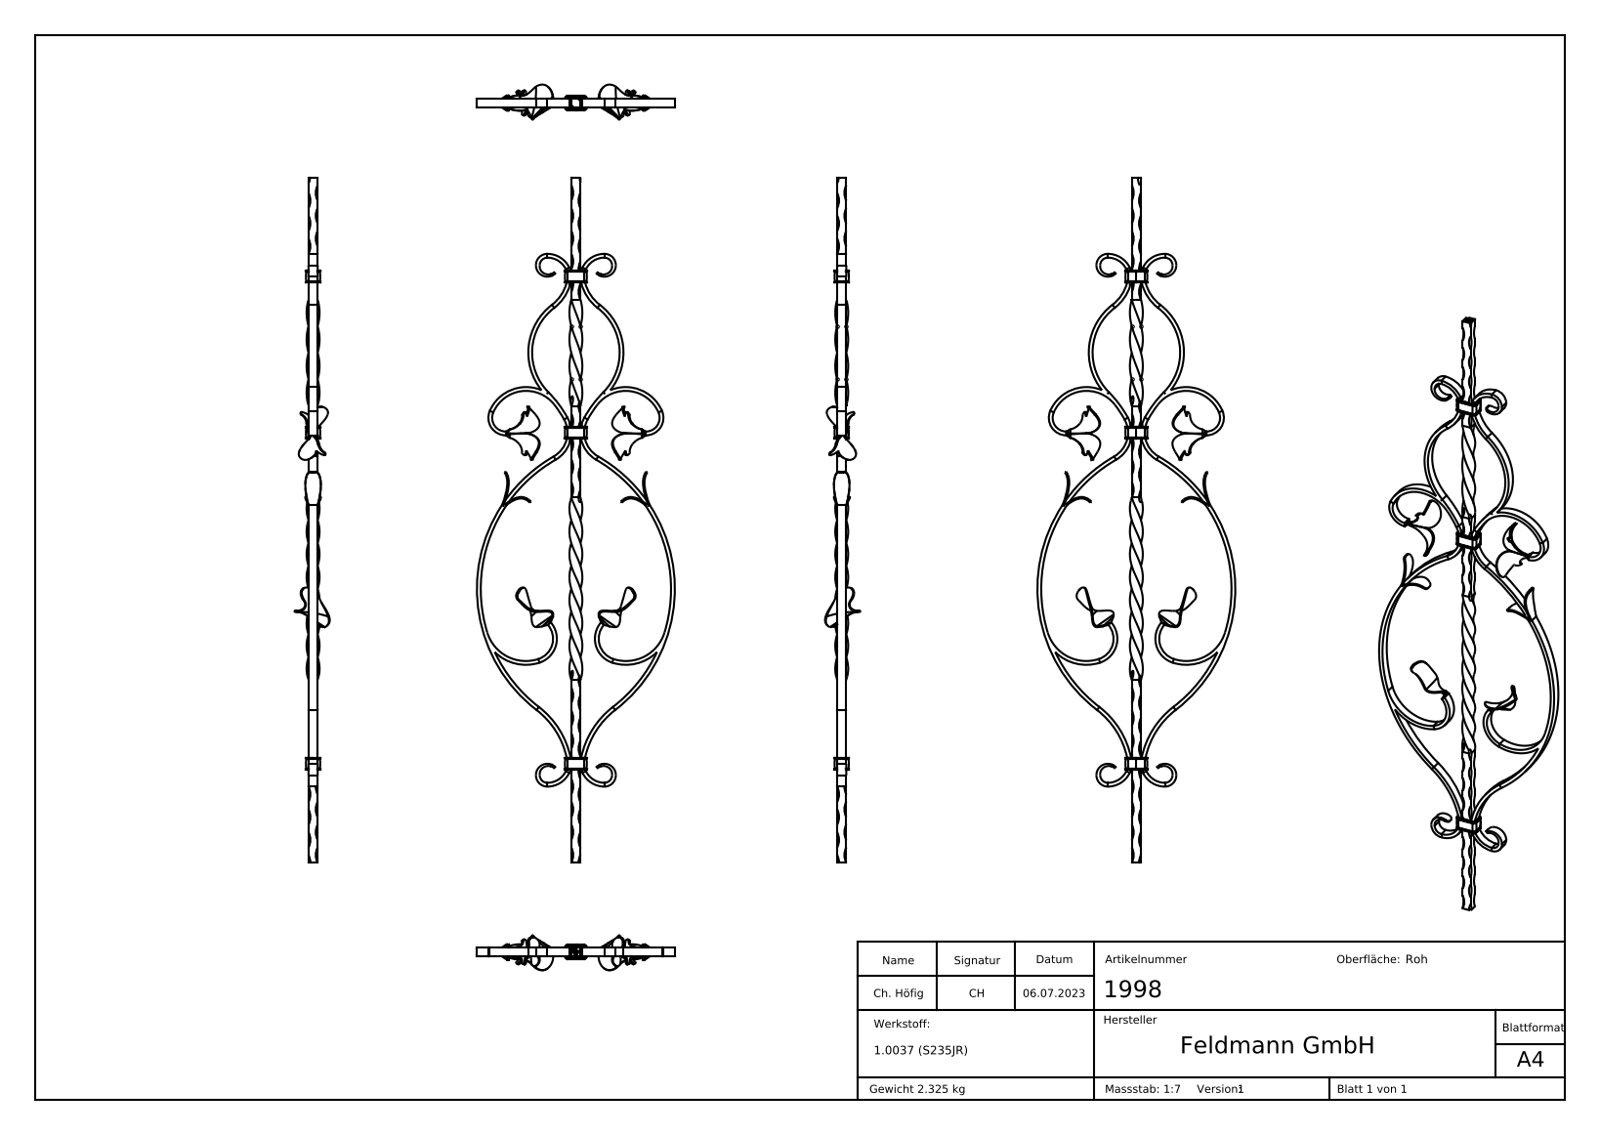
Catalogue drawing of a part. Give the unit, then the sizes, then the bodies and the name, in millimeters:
Units: millimetres
Overall size (bounding box): 900 × 260 × 46.12
Partial cylindrical surfaces — rounded edges, fillets, slot ends (radius × count): R0.5 ×64, R0.2 ×24, R21.62 ×12, R5 ×8, R10 ×6, R1 ×4, R4 ×4, R15 ×4
Main face-to-face distances: 12, 12.5, 0.5, 13, 5.5, 17.5, 16, 23, 435, 205
Volume: 298 260 mm³ · Surface area: 156 522 mm²
Bodies: 6 solids, 1117 faces (368 planar, 269 cylindrical, 480 other)
Part name (STEP PRODUCT): 1998
STEP written by: SolidWorks 2018 (CONFIG_CONTROL_DESIGN)
